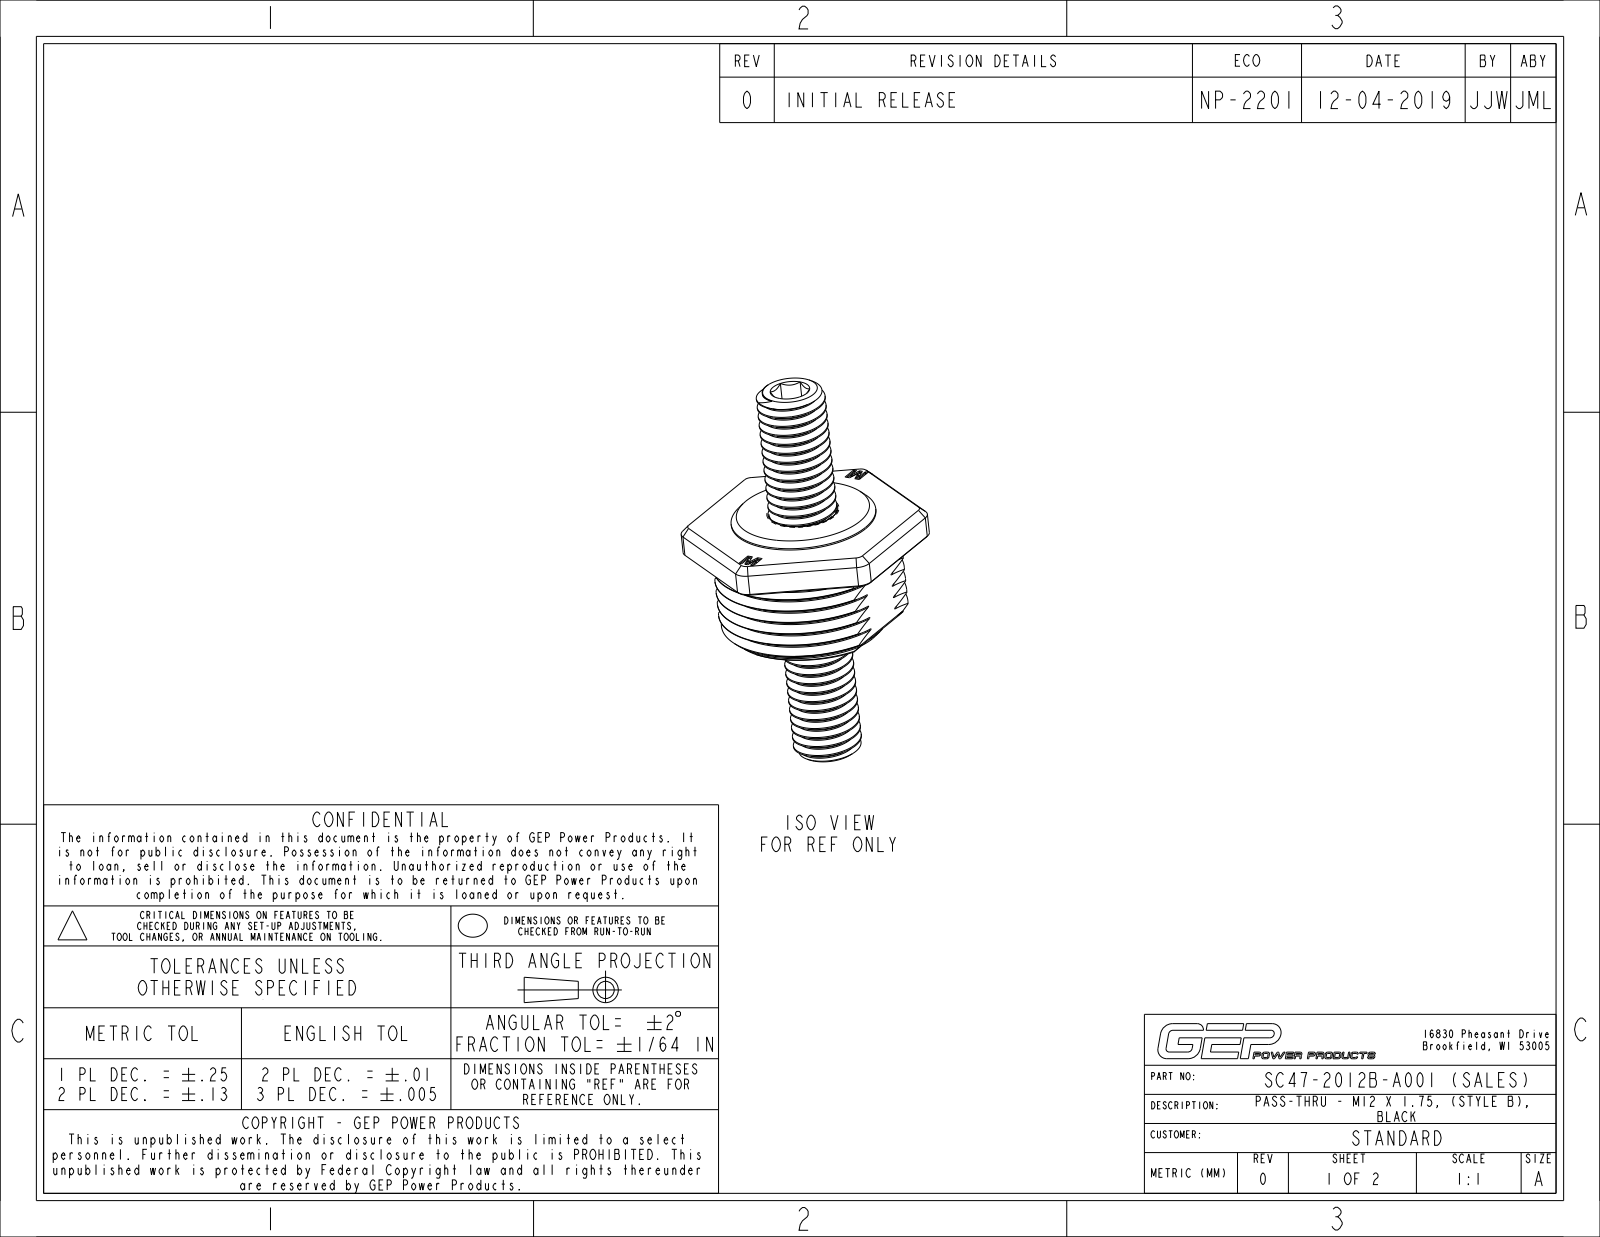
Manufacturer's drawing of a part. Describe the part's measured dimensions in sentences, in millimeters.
The part is named "SC47-2012B-A001_NCF_SW0001". Its 3-D file was written by "CREO PARAMETRIC BY PTC INC, 2017110 (CONFIG_CONTROL_DESIGN)". It is 1 solid with 358 faces: 83 planar, 134 cylindrical and 141 other. Overall it measures 70 by 43.21 by 38.1 millimeters. Its volume is 22 605 cubic millimeters and its surface area 10 002 square millimeters. Round holes: 1 of diameter 10.2. Round bosses or shafts: 1 of diameter 25.4, 1 of diameter 12. Partial cylindrical surfaces (rounded edges, fillets, slot ends): 16 of radius 0.13, 6 of radius 2.54, 2 of radius 0.76, 1 of radius 16.57. The main face-to-face distances are 1.27, 21.59, 6.35, 5.08, 16.51, 22.86, 15.24, 38.1, 28.58, 20.32.
